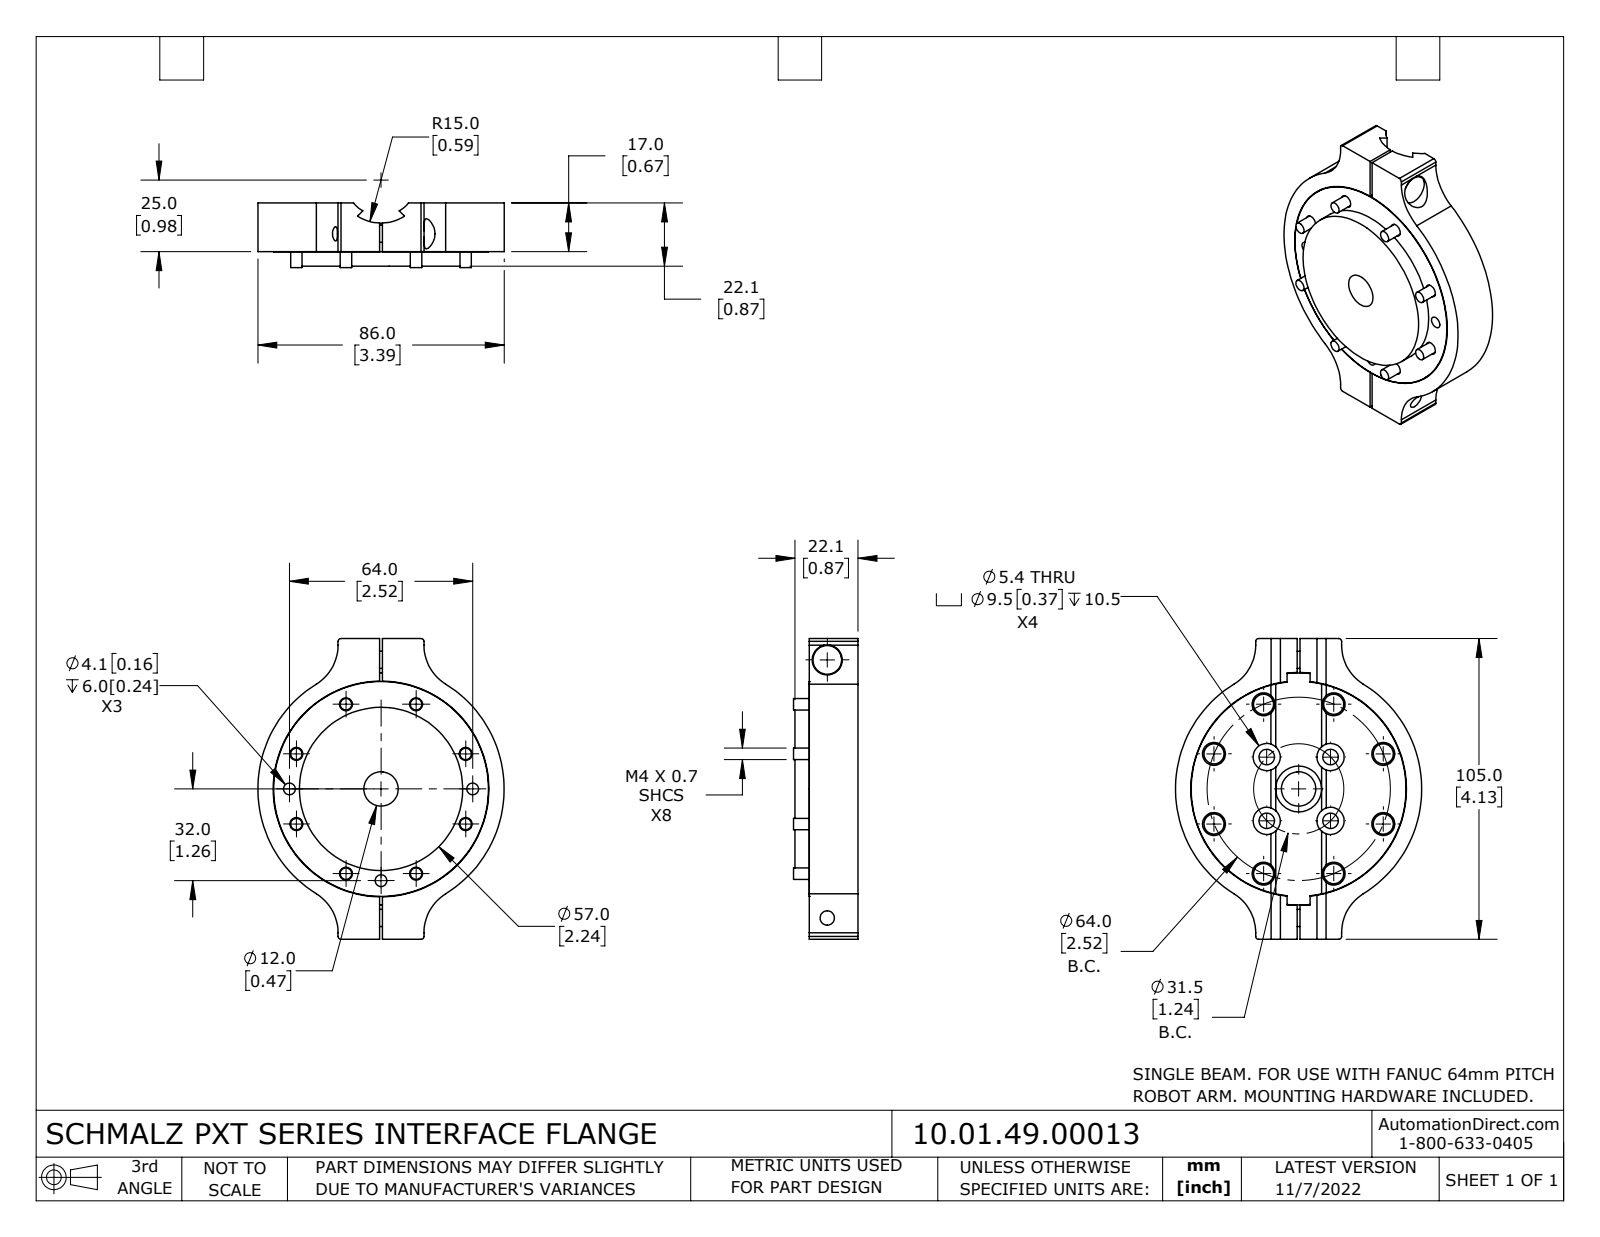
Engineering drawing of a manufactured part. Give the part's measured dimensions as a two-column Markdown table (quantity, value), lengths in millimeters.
| quantity | value |
| --- | --- |
| part name | 10.01.49.00013 |
| STEP written by | SolidWorks 2021 (CONFIG_CONTROL_DESIGN) |
| units | millimeters |
| bodies | 14 solids, 260 faces (85 planar, 163 cylindrical, 12 other) |
| overall size | 105 × 86 × 22.55 |
| volume | 103 887 mm³ |
| surface area | 46 026 mm² |
| round holes (diameter × count) | 4.5 × 8, 8 × 8, 5.4 × 4, 9.5 × 4, 4.1 × 3, 5.1 × 3, 5 × 2, 6.3 × 2, 10.5 × 2, 12 × 1, 16 × 1, 75.3 × 1 |
| round bosses / shafts (diameter × count) | 7 × 8, 4 × 8, 10 × 2, 6 × 2, 81 × 1, 75 × 1, 57 × 1 |
| partial cylindrical surfaces (radius × count) | 1 × 4, 16 × 4, 12.5 × 1, 12.55 × 1, 15 × 1, 15.05 × 1, 43 × 1 |
| main face-to-face distances | 17, 5, 22, 16.95, 5.05, 7.5, 9.5, 7.45, 12.5, 9.55 |
| hole center spacings | 29.77, 40.72, 46.94, 32, 45.25, 18.45, 15.75, 12.06 |
